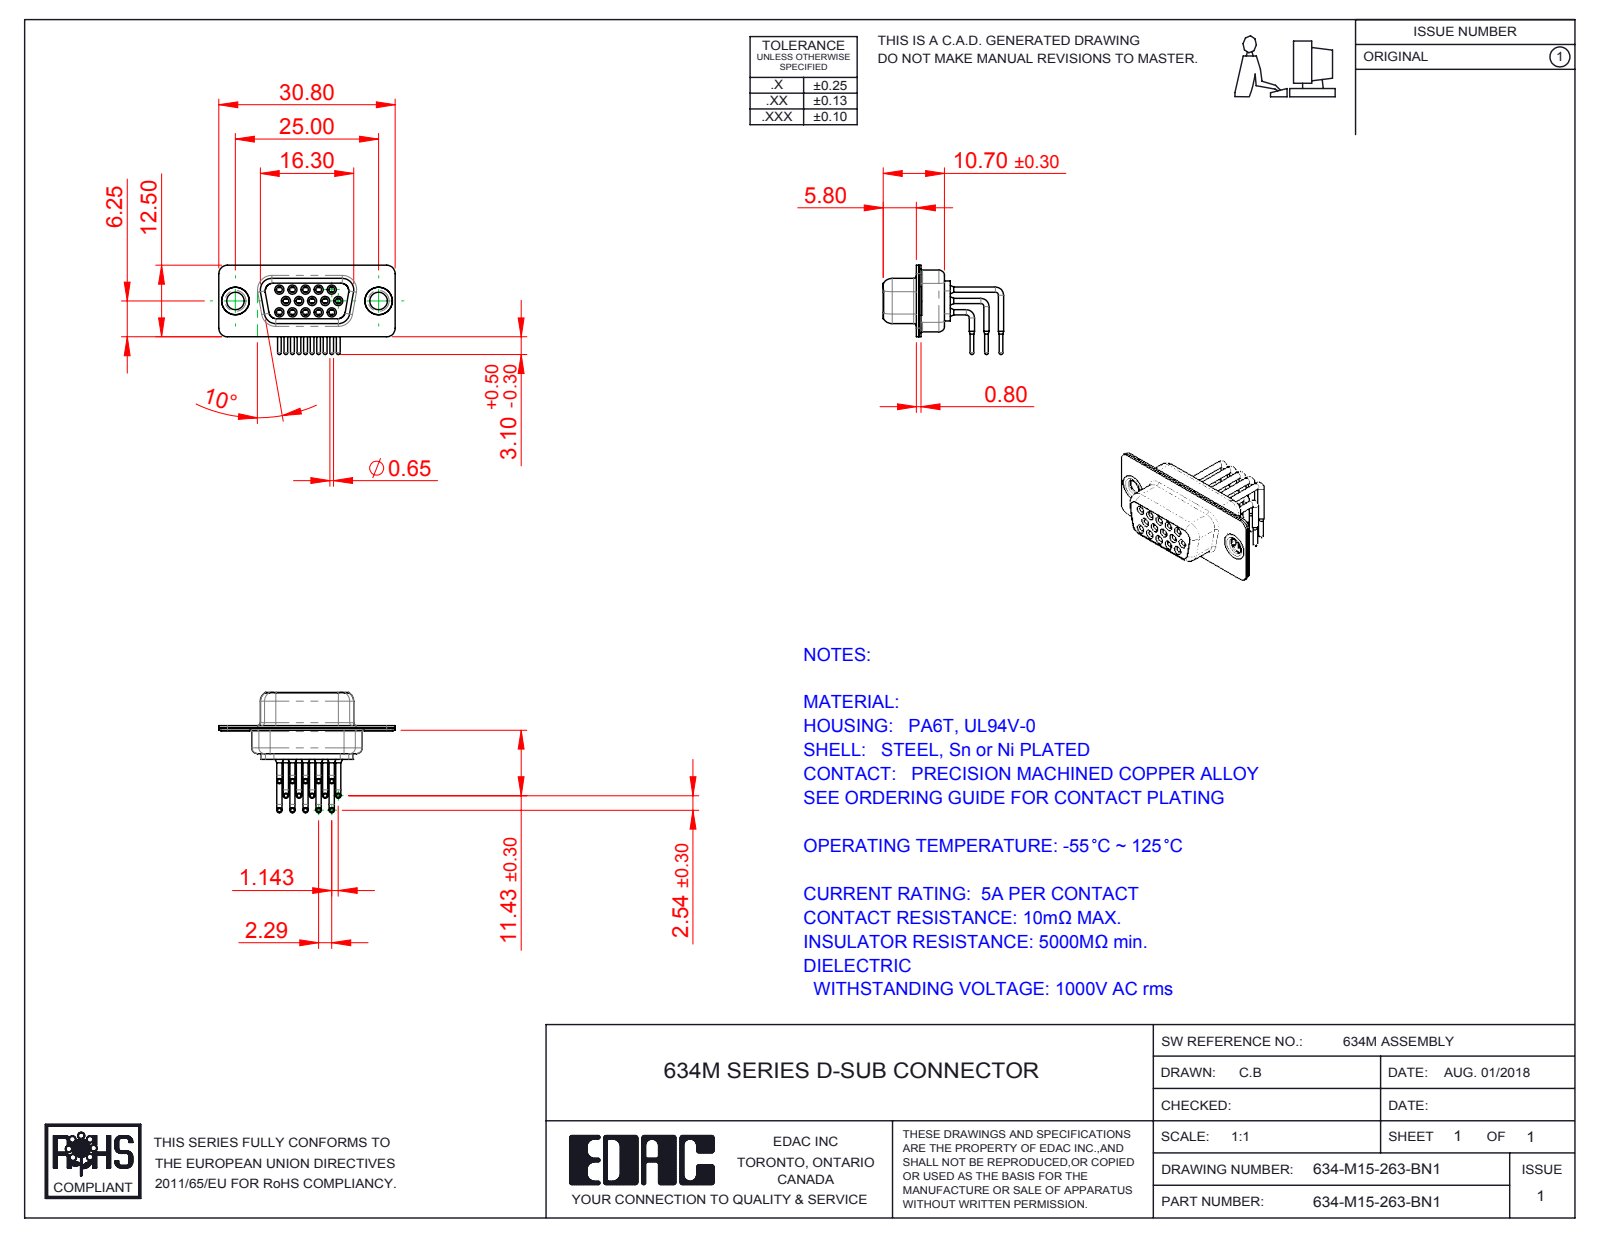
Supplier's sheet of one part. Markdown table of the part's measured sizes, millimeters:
| quantity | value |
| --- | --- |
| part name | 634M Contact Row 1; 634M Contact Row 3; 634M Contact Row 2; 634M Shell Rear_15 Contacts (+4 more) |
| STEP written by | SolidWorks 2016 (CONFIG_CONTROL_DESIGN) |
| units | millimeters |
| bodies | 20 solids, 1048 faces (292 planar, 466 cylindrical, 290 other) |
| overall size | 30.8 × 21.02 × 15.6 |
| volume | 1 661 mm³ |
| surface area | 5 524 mm² |
| round holes (diameter × count) | 1 × 15, 1.1 × 15, 1.7 × 15, 1.8 × 15, 2 × 15, 3.05 × 2, 4 × 2, 4.8 × 2 |
| round bosses / shafts (diameter × count) | 0.9 × 30, 1.6 × 15, 1.5 × 15, 0.65 × 15, 5 × 2, 4.9 × 2, 3.55 × 2, 2 × 1 |
| partial cylindrical surfaces (radius × count) | 1.5 × 16, 2 × 12, 1.35 × 8, 1.6 × 8, 0.25 × 4, 0.5 × 4, 0.6 × 4, 0.65 × 4 |
| main face-to-face distances | 0.4, 0.8, 1.45, 2.3, 8.95, 1.9, 8.5, 0.85, 6.2, 9.35 |
| hole center spacings | 2.28, 3.96, 2.29, 4.57, 6.05, 6.04, 6.86, 7.92 |
